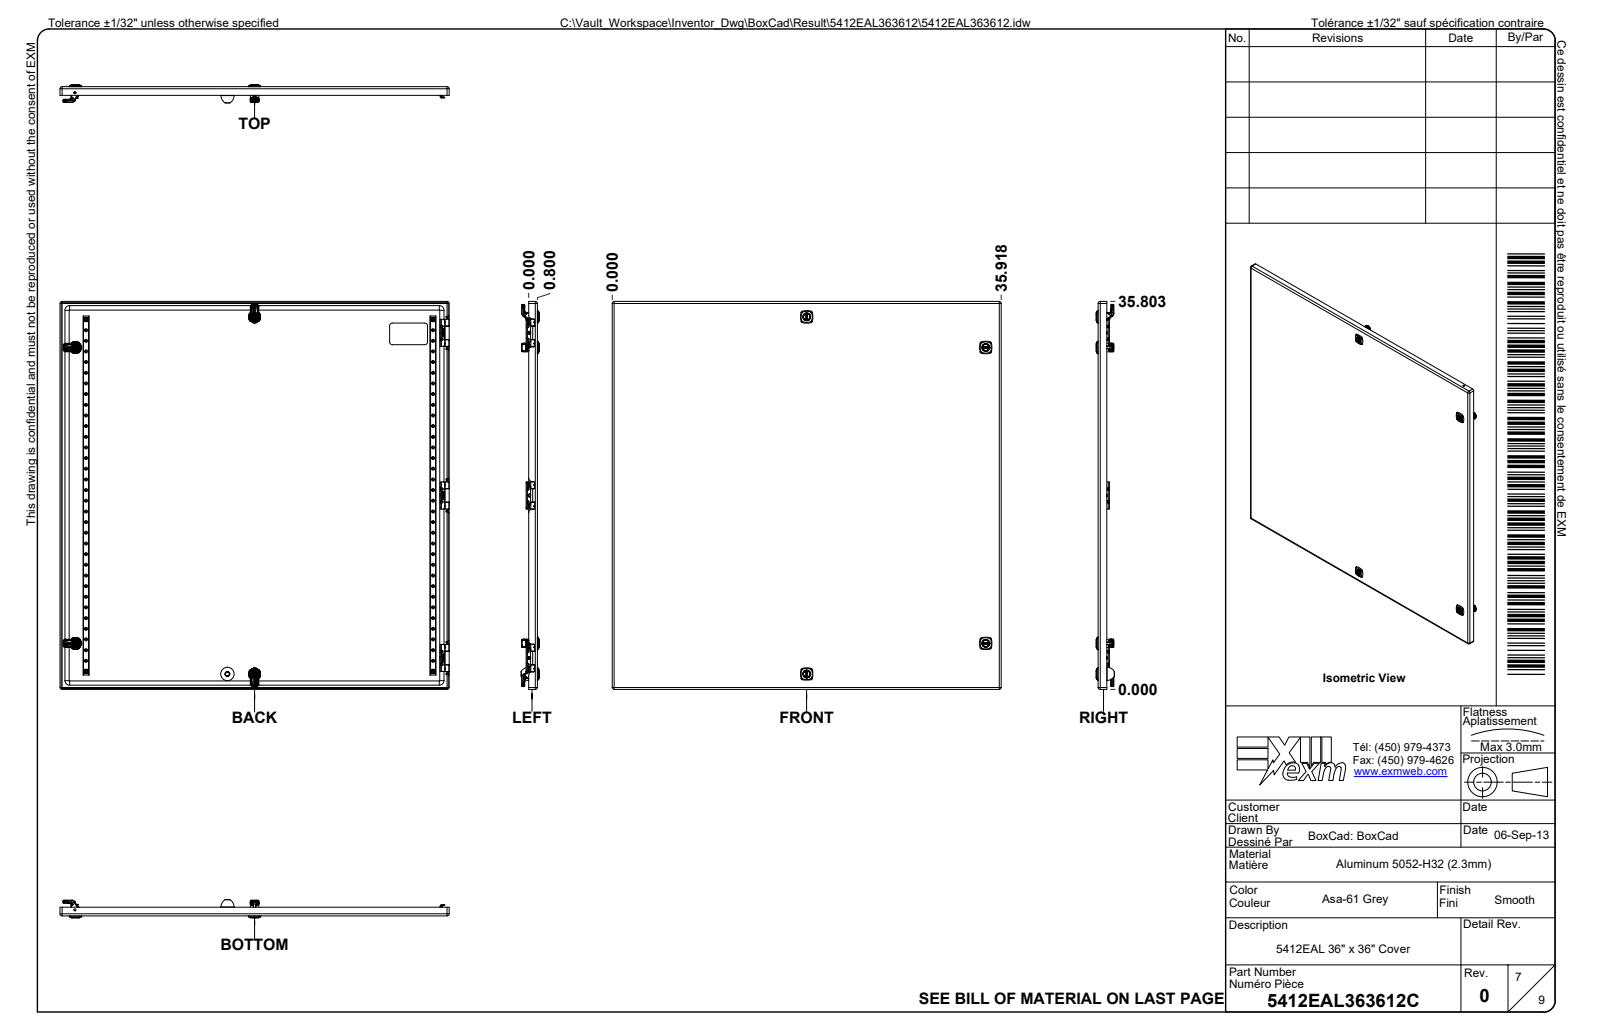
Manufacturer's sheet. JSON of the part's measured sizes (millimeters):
{"part_name": "5412EAL363612; 5412EAL363612B; 5412EAL363612B-P; STK-Q-16010 (+8 more)", "step_written_by": "Autodesk Inventor 2024 (AUTOMOTIVE_DESIGN)", "units": "millimeters", "bodies": {"solids": 103, "faces": 11062, "planar": 5405, "cylindrical": 2087, "other": 3570}, "overall_size": [915.5, 914.4, 336.3], "volume_mm3": 9300000, "surface_area_mm2": 7950000, "round_holes": [[4.2, 64], [0.8, 14], [5.1, 11], [8, 10], [12.7, 9], [6.9, 8], [7.9, 8], [7.4, 7], [1.1, 6], [5, 4], [6.8, 4], [9.9, 4]], "round_bosses_or_shafts": [[6, 64], [0.8, 14], [5.9, 13], [1, 12], [7.9, 8], [18.2, 6], [19.7, 4], [19.5, 4]], "partial_cylinders_radius": [[0.5, 162], [1, 136], [0.2, 120], [0.3, 92], [0.3, 56], [0.8, 38], [0.4, 37], [0.3, 32]], "face_to_face_distances": [2.3, 329.6, 912.1, 327.4, 331.9, 24.5, 22.2, 305.2, 307.4, 2.7], "hole_center_spacings": [50, 25, 75, 100, 125, 150, 409.6, 439.1]}
